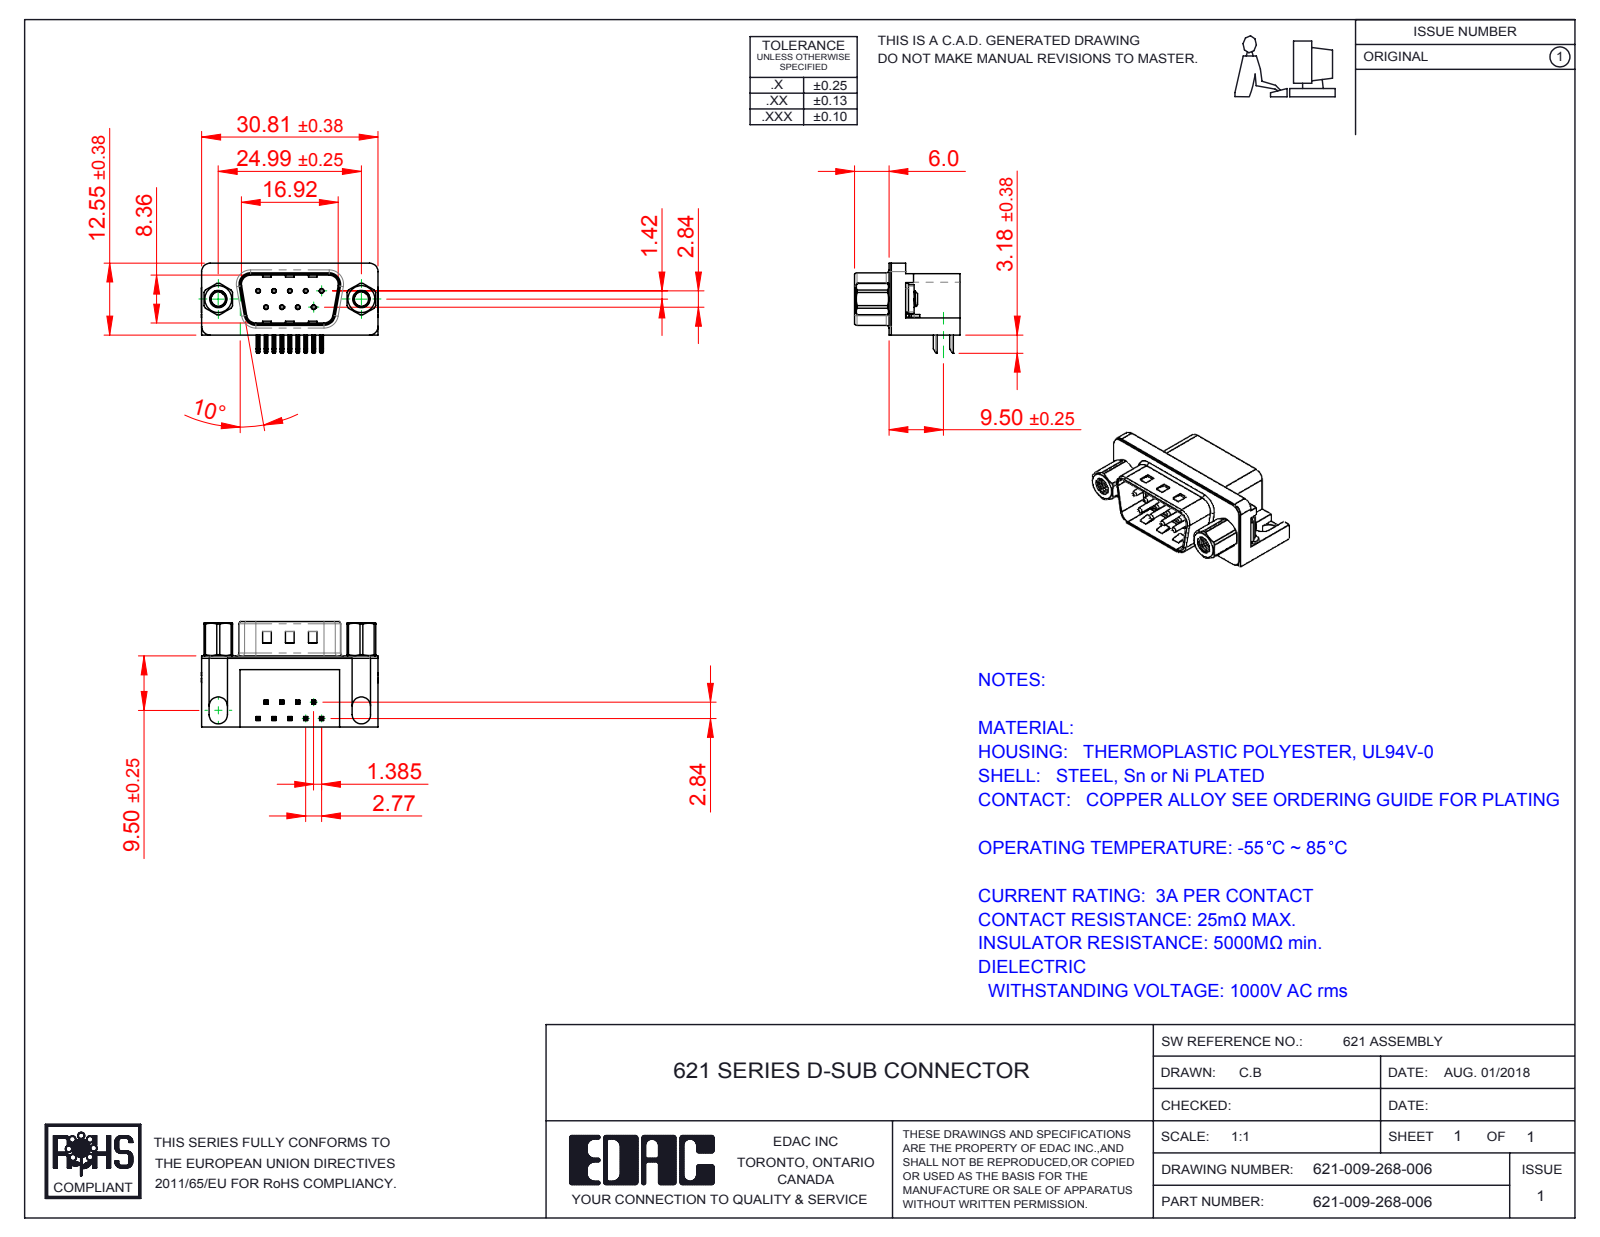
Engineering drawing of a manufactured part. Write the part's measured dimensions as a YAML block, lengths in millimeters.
part_name: "621 Shell_9 Socket; 621-009-268-006; 621 Housing_9 Socket; 621 M3 Threaded Rivet (+4 more)"
step_written_by: "SolidWorks 2016 (CONFIG_CONTROL_DESIGN)"
units: millimeters
bodies: {solids: 17, faces: 1133, planar: 593, cylindrical: 407, other: 133}
overall_size: [30.89, 18.4, 15.73]
volume: 3449
surface_area: 4780
round_holes:
  - {diameter: 0.35, count: 9}
  - {diameter: 0.8, count: 9}
  - {diameter: 2.5, count: 2}
  - {diameter: 4, count: 2}
  - {diameter: 4.8, count: 2}
  - {diameter: 5, count: 2}
round_bosses_or_shafts:
  - {diameter: 0.75, count: 9}
  - {diameter: 4.9, count: 2}
  - {diameter: 4.75, count: 2}
  - {diameter: 3.9, count: 2}
  - {diameter: 3, count: 2}
partial_cylinders:
  - {radius: 0.25, count: 44}
  - {radius: 0.12, count: 18}
  - {radius: 1, count: 16}
  - {radius: 0.5, count: 9}
  - {radius: 1.5, count: 8}
  - {radius: 1.6, count: 8}
  - {radius: 0.9, count: 4}
  - {radius: 2, count: 4}
face_to_face_distances: [0.4, 12, 12.4, 10.35, 9.5, 2.5, 2.9, 2.1, 0.35, 10.7]
hole_center_spacings: [3.16, 2.77, 5.54, 5.03, 5.04, 8.31, 7.48, 7.49]
